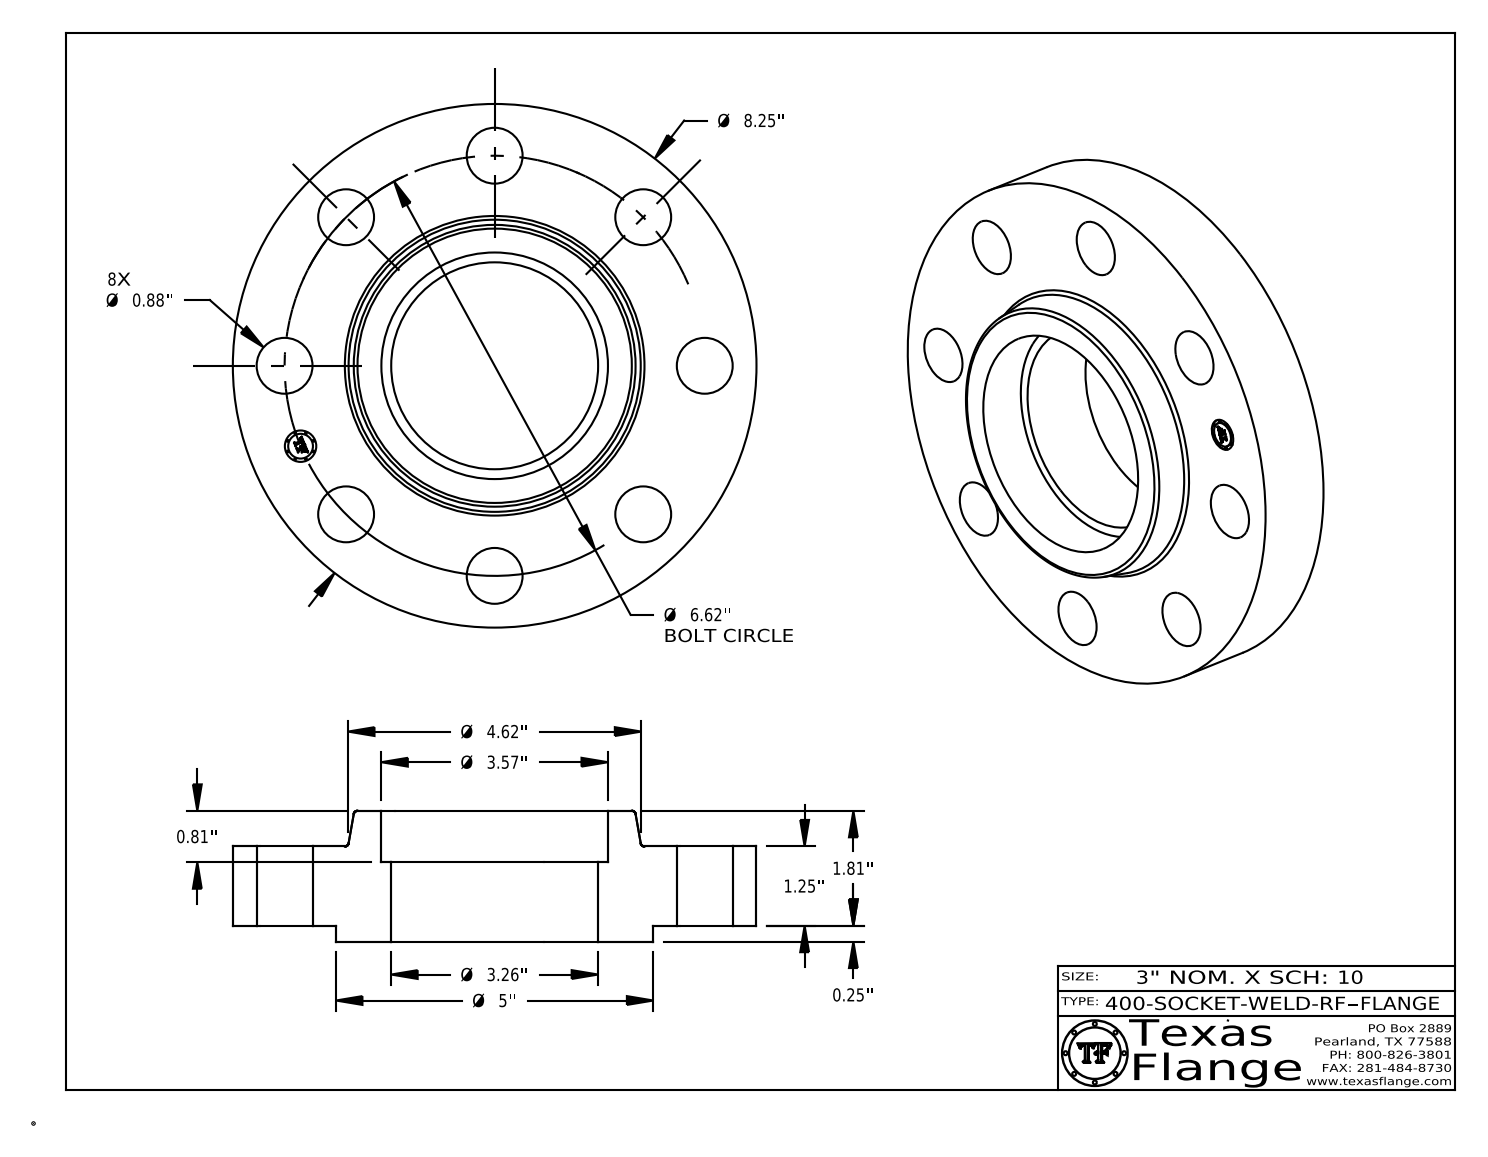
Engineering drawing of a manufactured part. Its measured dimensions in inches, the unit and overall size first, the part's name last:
Units: inches
Overall size (bounding box): 8.25 × 8.25 × 2.06
Round holes (diameter × count): ⌀0.88 ×8, ⌀0.495 ×1, ⌀3.26 ×1, ⌀3.57 ×1
Round bosses / shafts (diameter × count): ⌀0.03 ×8, ⌀8.25 ×1, ⌀5 ×1, ⌀0.39 ×1
Main face-to-face distances: 1.25, 0.25, 1.5, 2.06, 1.81, 0.56, 1, 0.81, 0.015, 1.485
Hole centre spacings: 3.31, 2.533, 6.116, 4.681, 4.681, 1.291, 3.678, 6.493
Volume: 56.1 in³ · Surface area: 172.6 in²
Bodies: 1 solid, 420 faces (370 planar, 44 cylindrical, 6 other)
Part name (STEP PRODUCT): 400-SOCKET-WELD-RF
STEP written by: CATIA V5 STEP AP214 (AUTOMOTIVE_DESIGN)
